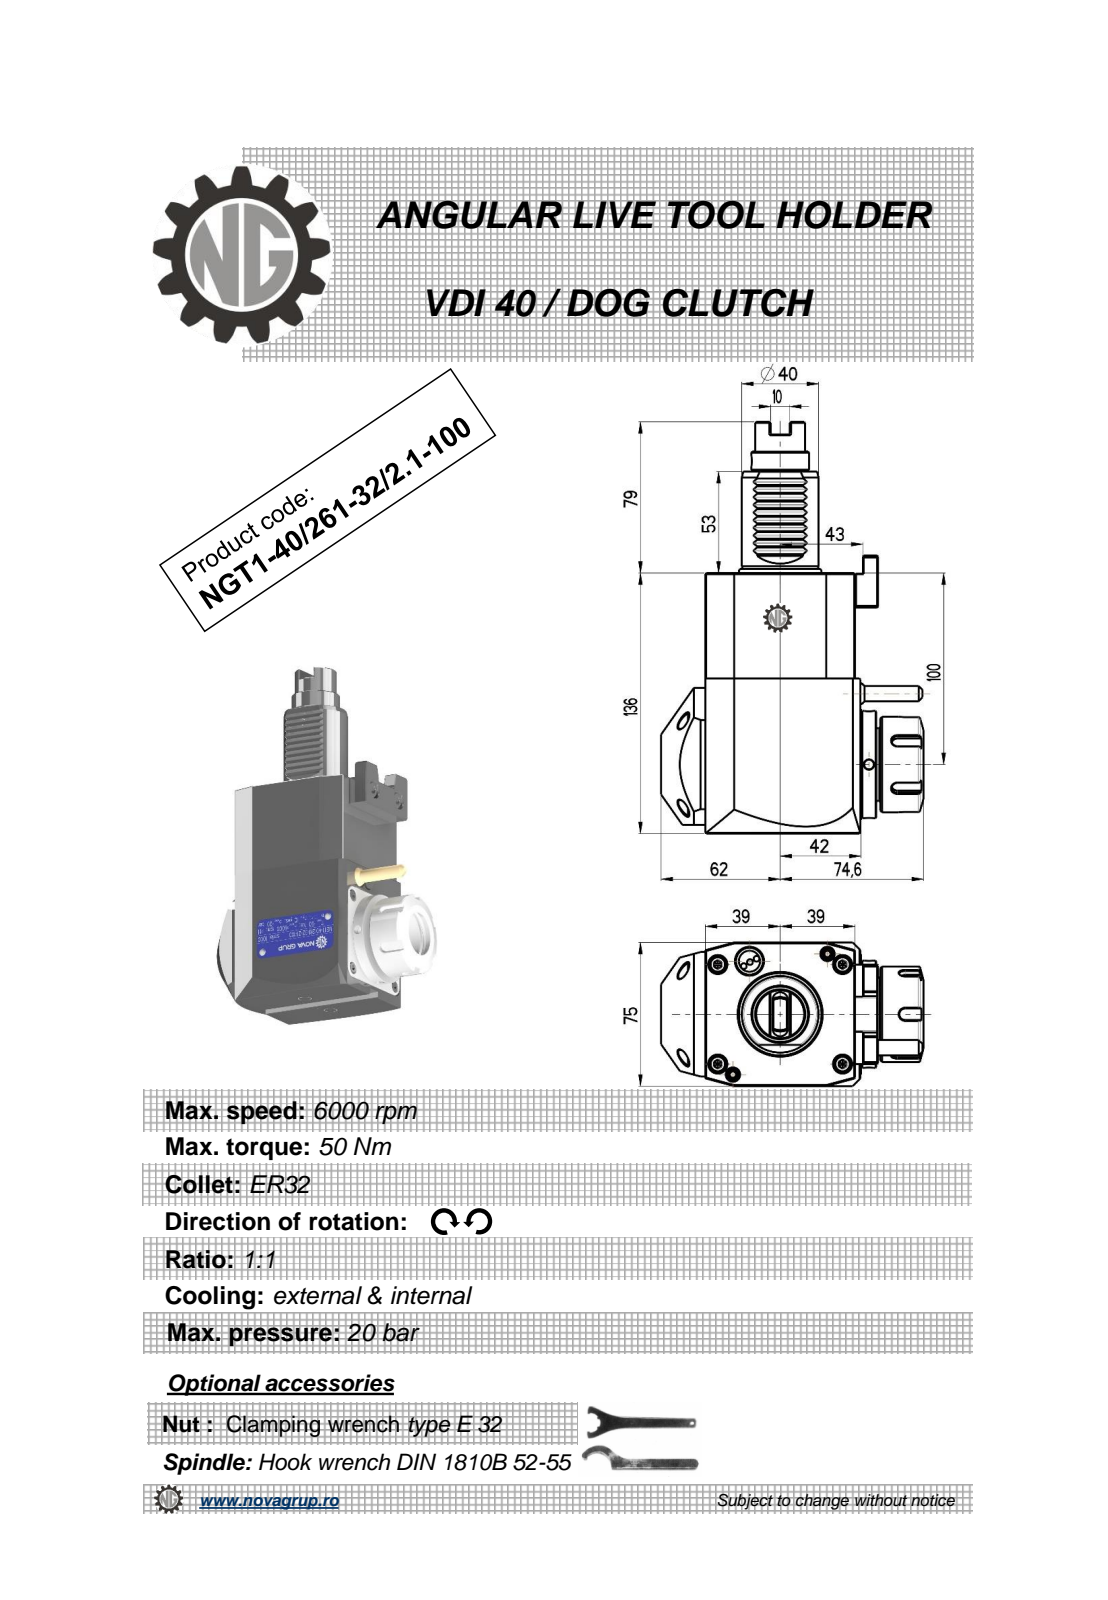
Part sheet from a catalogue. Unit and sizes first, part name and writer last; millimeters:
Units: millimetres
Overall size (bounding box): 215 × 136.6 × 75
Round holes (diameter × count): ⌀5 ×3, ⌀3 ×1, ⌀4.2 ×1, ⌀27 ×1
Round bosses / shafts (diameter × count): ⌀56 ×1, ⌀50 ×1, ⌀43 ×1, ⌀41 ×1, ⌀40 ×1, ⌀30 ×1, ⌀26 ×1, ⌀11.2 ×1
Partial cylindrical surfaces — rounded edges, fillets, slot ends (radius × count): R0.3 ×10, R0.22 ×6, R3 ×5, R0.5 ×3, R1 ×2, R12.5 ×1, R40 ×1
Main face-to-face distances: 75, 136, 78, 81, 0.5, 3, 84.88, 1, 80.8, 2.8
Hole centre spacings: 40.93, 122.75, 158.5
Volume: 1 015 000 mm³ · Surface area: 78 061 mm²
Bodies: 1 solid, 375 faces (192 planar, 68 cylindrical, 115 other)
Part name (STEP PRODUCT): NGT1_40_261_32_2_1_100
STEP written by: PRO/ENGINEER BY PARAMETRIC TECHNOLOGY CORPORATION, 2010280 (CONFIG_CONTROL_DESIGN)
